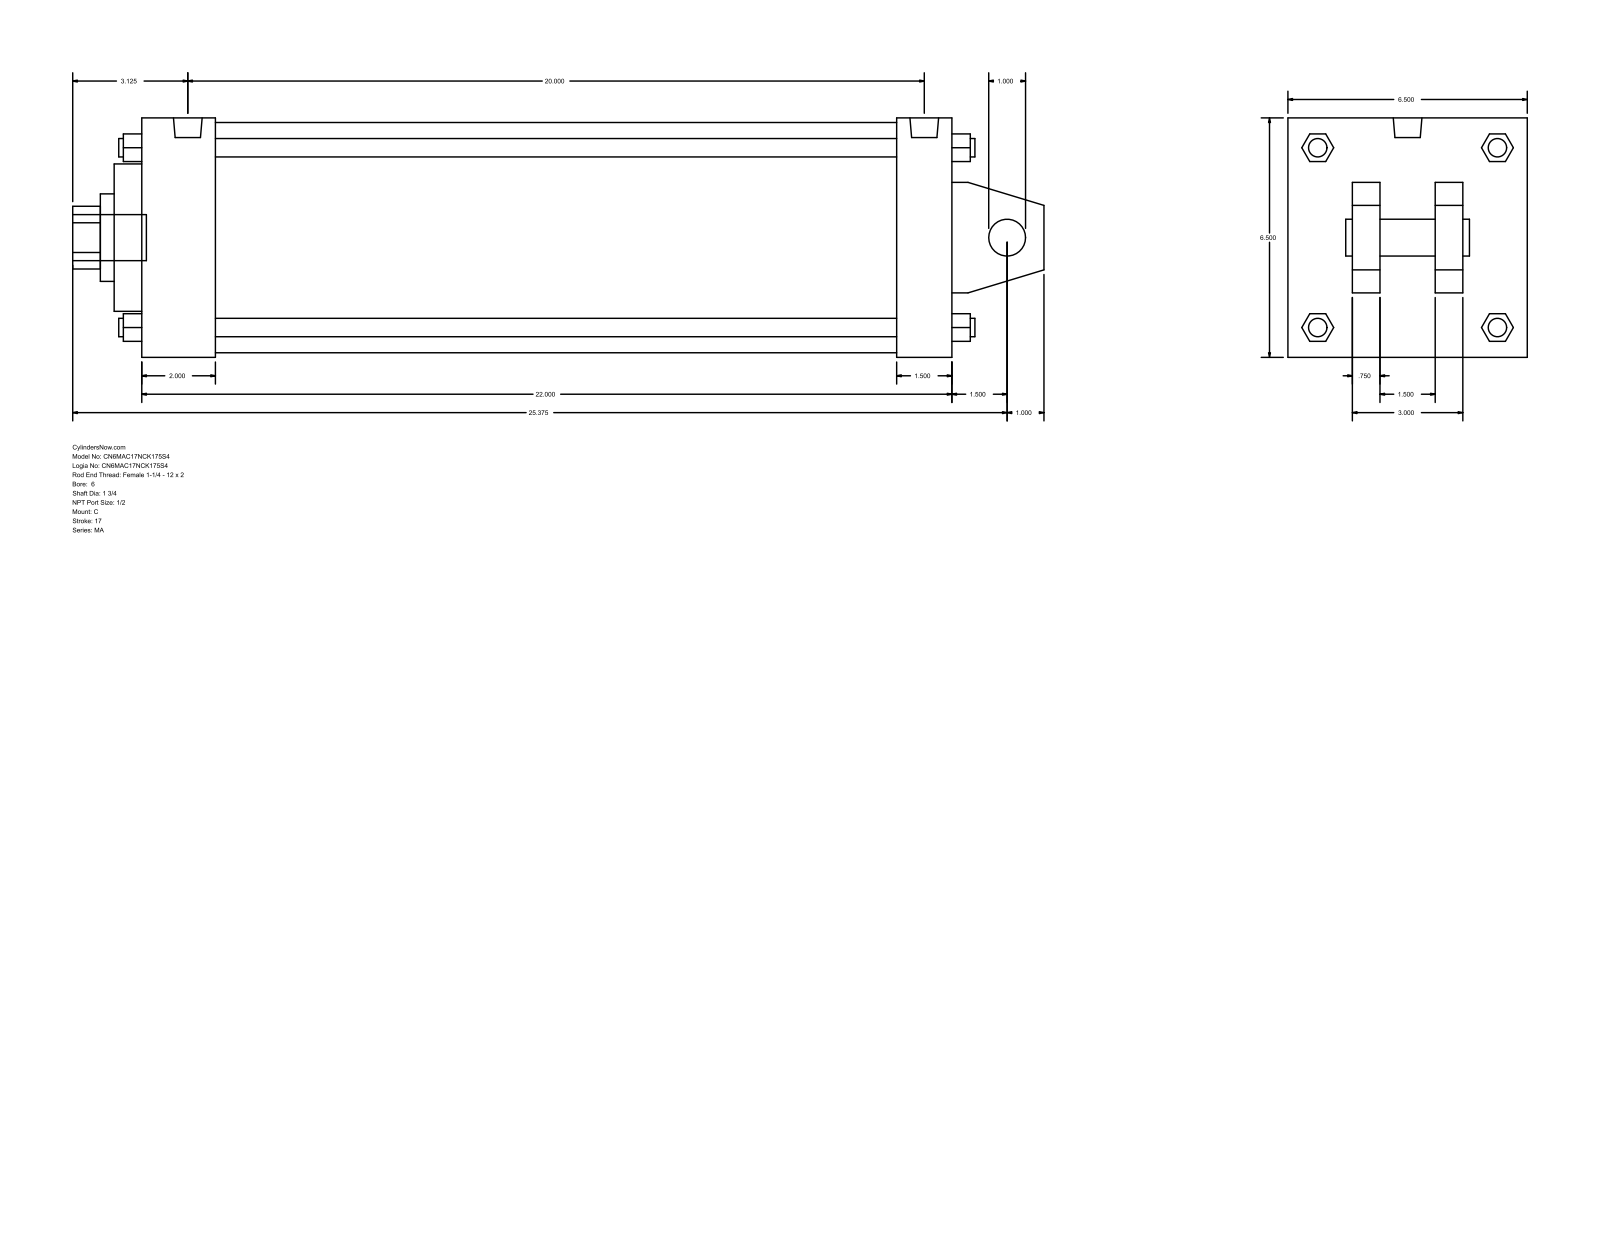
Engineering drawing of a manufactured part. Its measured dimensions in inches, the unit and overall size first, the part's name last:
Units: inches
Overall size (bounding box): 26.375 × 6.5 × 6.5
Round holes (diameter × count): ⌀1 ×1, ⌀1.75 ×1, ⌀2.375 ×1, ⌀4 ×1, ⌀6.25 ×1
Round bosses / shafts (diameter × count): ⌀0.687 ×4, ⌀0.5 ×4, ⌀0.778 ×2, ⌀1.25 ×1
Partial cylindrical surfaces — rounded edges, fillets, slot ends (radius × count): R0.852 ×1
Main face-to-face distances: 6.5, 22, 0.75, 2.5, 4, 2, 1.75, 4.75, 2.25, 20
Bodies: 0 solids, 141 faces (109 planar, 32 cylindrical, 0 other)
Part name (STEP PRODUCT): MA_C__0600_1.75
STEP written by: GSSL Pune (CONFIG_CONTROL_DESIGN)
